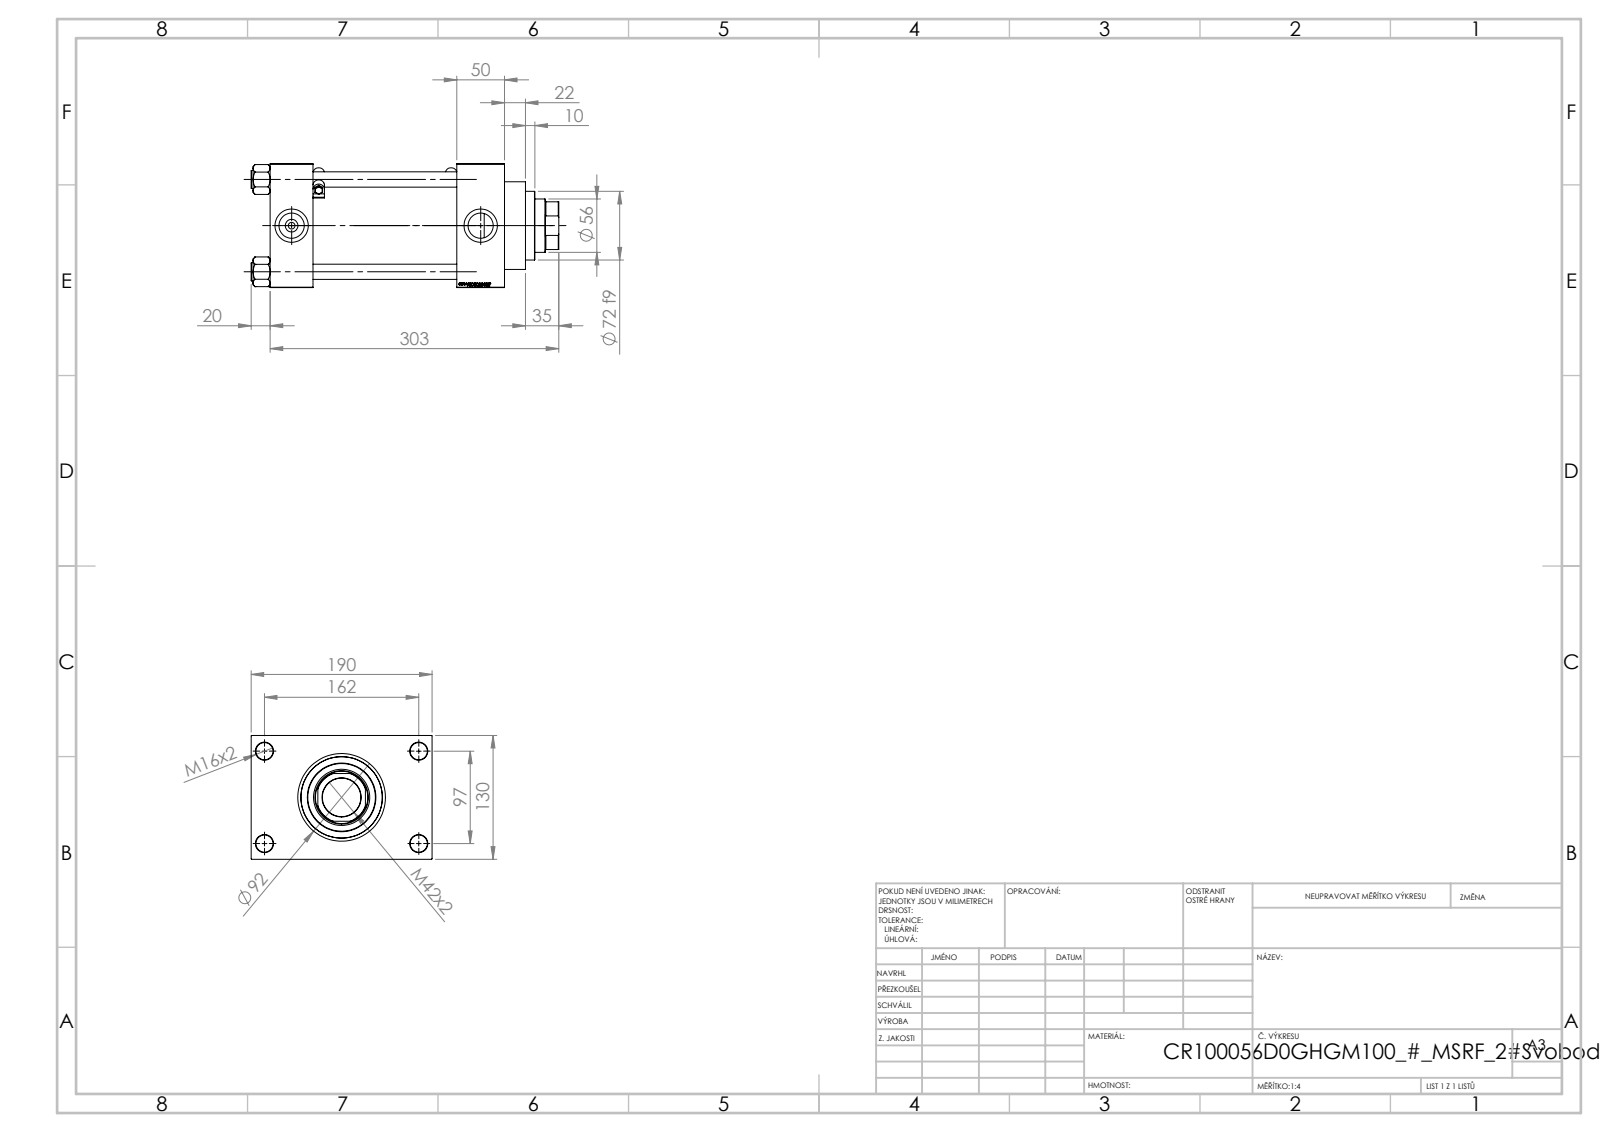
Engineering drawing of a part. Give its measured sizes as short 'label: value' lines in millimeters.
name: NUT_M5_D; V215CR_VCP_D; V215CR_D_Body; V215_VC_A (+2 more)
written by: SolidWorks 2019 (CONFIG_CONTROL_DESIGN)
unit: mm
bodies: 13 solids, 1215 faces (581 planar, 116 cylindrical, 518 other)
size: 323 × 190 × 130
volume: 2 975 000 mm³; area: 449 005 mm²
holes: 4× ⌀16, 4× ⌀18, 2× ⌀7, 2× ⌀26.44, 2× ⌀35, 1× ⌀40.5, 1× ⌀56, 1× ⌀59, 1× ⌀76, 1× ⌀85.5, 1× ⌀100
bosses: 4× ⌀19, 2× ⌀5, 2× ⌀2.5, 1× ⌀106, 1× ⌀92, 1× ⌀72
rounds: 12× R0.5, 4× R6, 1× R27
face distances: 130, 50, 45, 196, 151, 246, 201, 30, 160, 190
hole spacings: 32.55, 68.52, 94.41, 96.9, 102.27, 129.45, 161.73, 97
